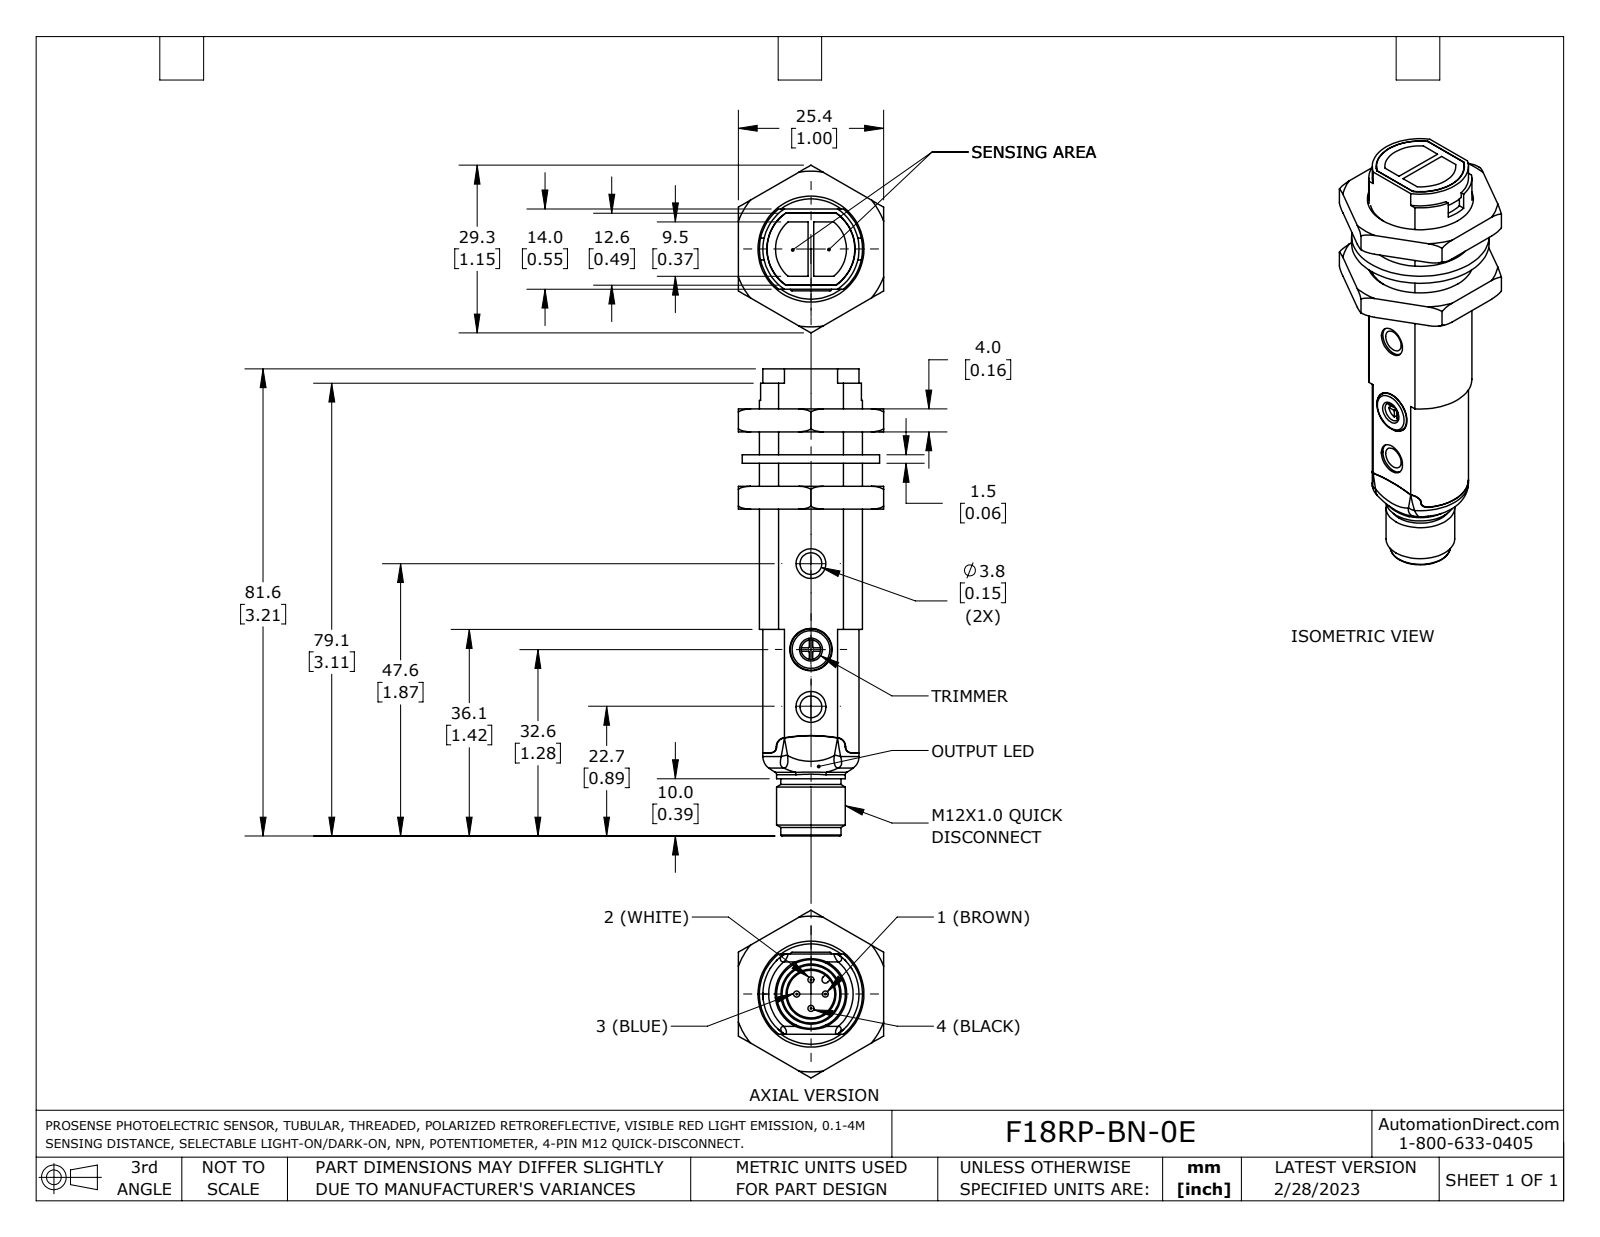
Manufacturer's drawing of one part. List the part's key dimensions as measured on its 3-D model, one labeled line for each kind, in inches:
Part name (STEP PRODUCT): F18RP-BP-0E
STEP written by: SolidWorks 2021 (AUTOMOTIVE_DESIGN)
Units: inches
Bodies: 4 solids, 202 faces (87 planar, 54 cylindrical, 61 other)
Overall size (bounding box): 3.211 × 1.153 × 0.998
Volume: 1.112 in³ · Surface area: 12.99 in²
Round holes (diameter × count): ⌀0.15 ×2, ⌀0.134 ×1, ⌀0.205 ×1, ⌀0.291 ×1, ⌀0.689 ×1
Round bosses / shafts (diameter × count): ⌀0.042 ×4, ⌀0.945 ×1, ⌀0.709 ×1, ⌀0.472 ×1, ⌀0.413 ×1, ⌀0.283 ×1
Partial cylindrical surfaces — rounded edges, fillets, slot ends (radius × count): R0.039 ×4, R0.059 ×4, R0.102 ×2, R1.102 ×2, R0.02 ×1, R0.024 ×1, R0.301 ×1, R0.303 ×1
Main face-to-face distances: 0.157, 0.374, 0.551, 0.531, 0.217, 0.315, 0.998, 0.689, 0.433, 0.059
Hole centre spacings: 0.394, 0.591, 0.984
